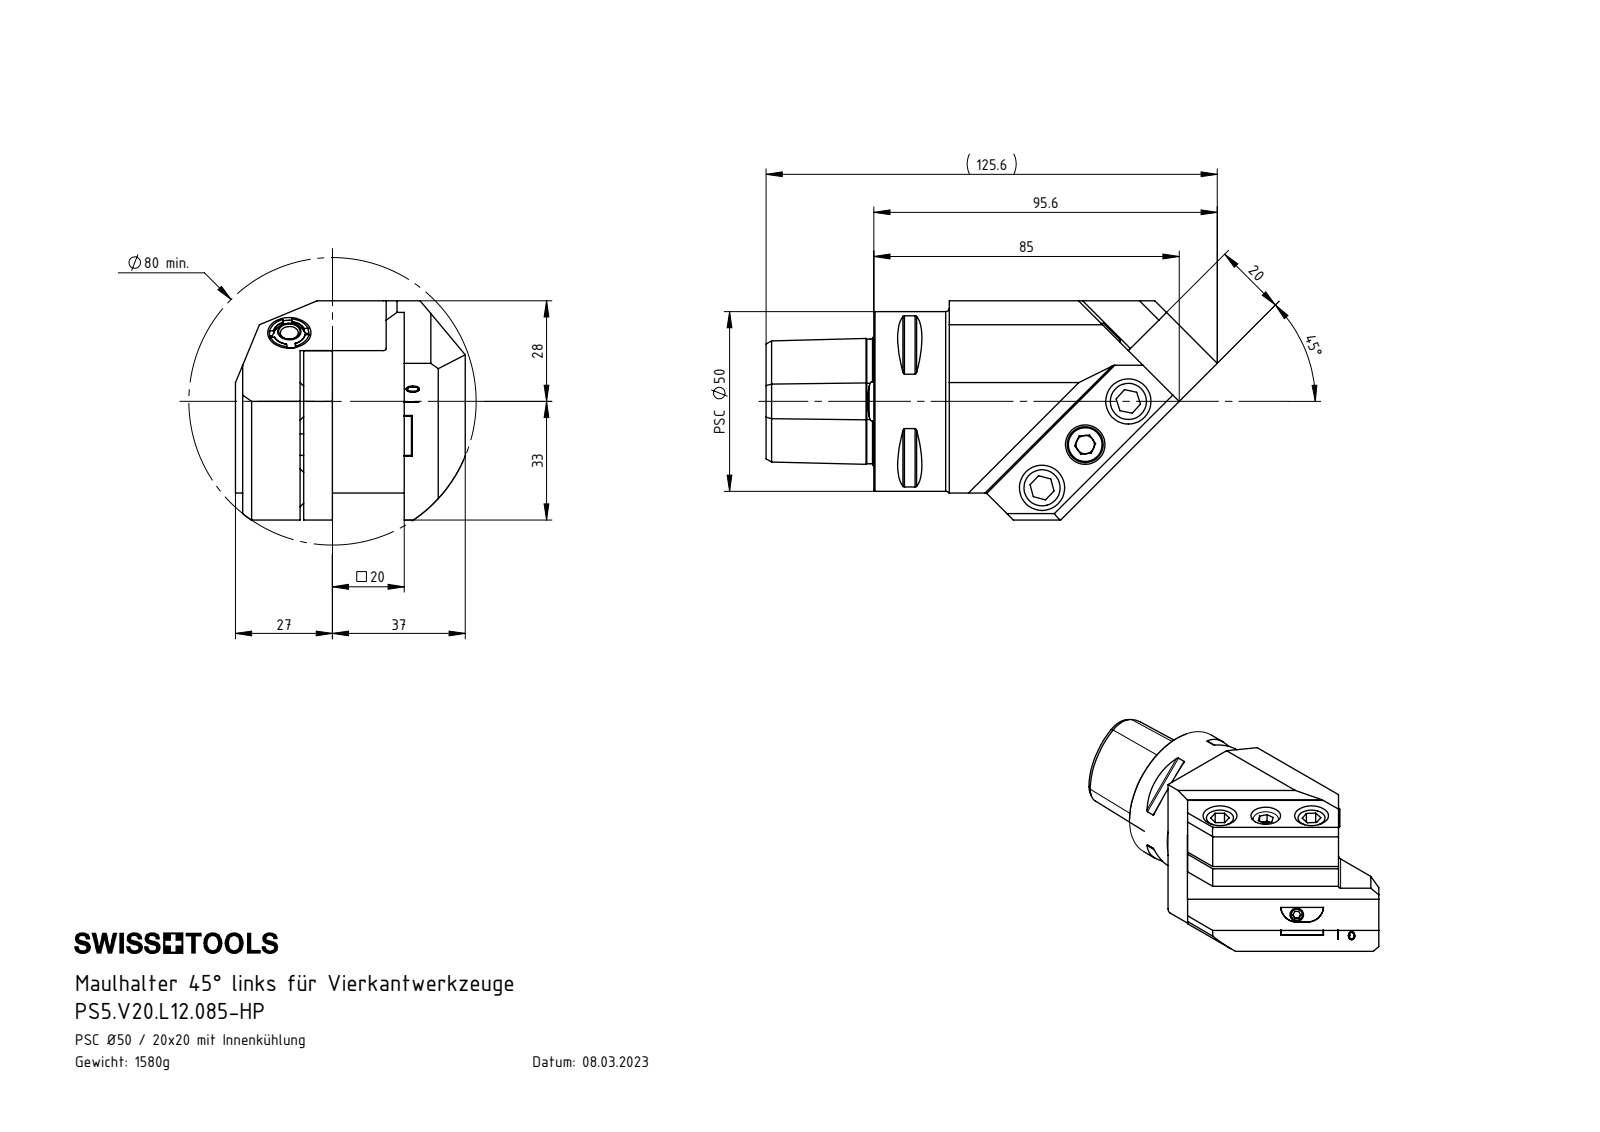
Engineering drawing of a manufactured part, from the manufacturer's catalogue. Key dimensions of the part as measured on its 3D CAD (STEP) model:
Part name (STEP PRODUCT): KVT_MB_600_050; ISO 4026 - M12 x 16; ISO 4026 - M5 x 5; ISO 4762 - M6 x 16 (+8 more)
STEP written by: SolidWorks 2017 (AUTOMOTIVE_DESIGN)
Units: millimetres
Bodies: 13 solids, 396 faces (135 planar, 83 cylindrical, 178 other)
Overall size (bounding box): 125.61 × 64 × 61
Volume: 201 327 mm³ · Surface area: 39 161 mm²
Round holes (diameter × count): ⌀5 ×4, ⌀4.2 ×2, ⌀10 ×2, ⌀10.2 ×2, ⌀11 ×2, ⌀4 ×1, ⌀6.1 ×1, ⌀6.8 ×1, ⌀8.5 ×1, ⌀14.5 ×1, ⌀16.3 ×1, ⌀21 ×1
Round bosses / shafts (diameter × count): ⌀12 ×3, ⌀5 ×2, ⌀50 ×1, ⌀10 ×1, ⌀6 ×1
Partial cylindrical surfaces — rounded edges, fillets, slot ends (radius × count): R0.5 ×8, R0.8 ×2, R6 ×2, R4.4 ×1, R5 ×1, R40 ×1
Main face-to-face distances: 20, 17, 45, 8, 28, 37, 1, 9, 46, 29
Hole centre spacings: 17, 26, 34, 42.31, 48.36, 58.86, 65.4, 73.83
